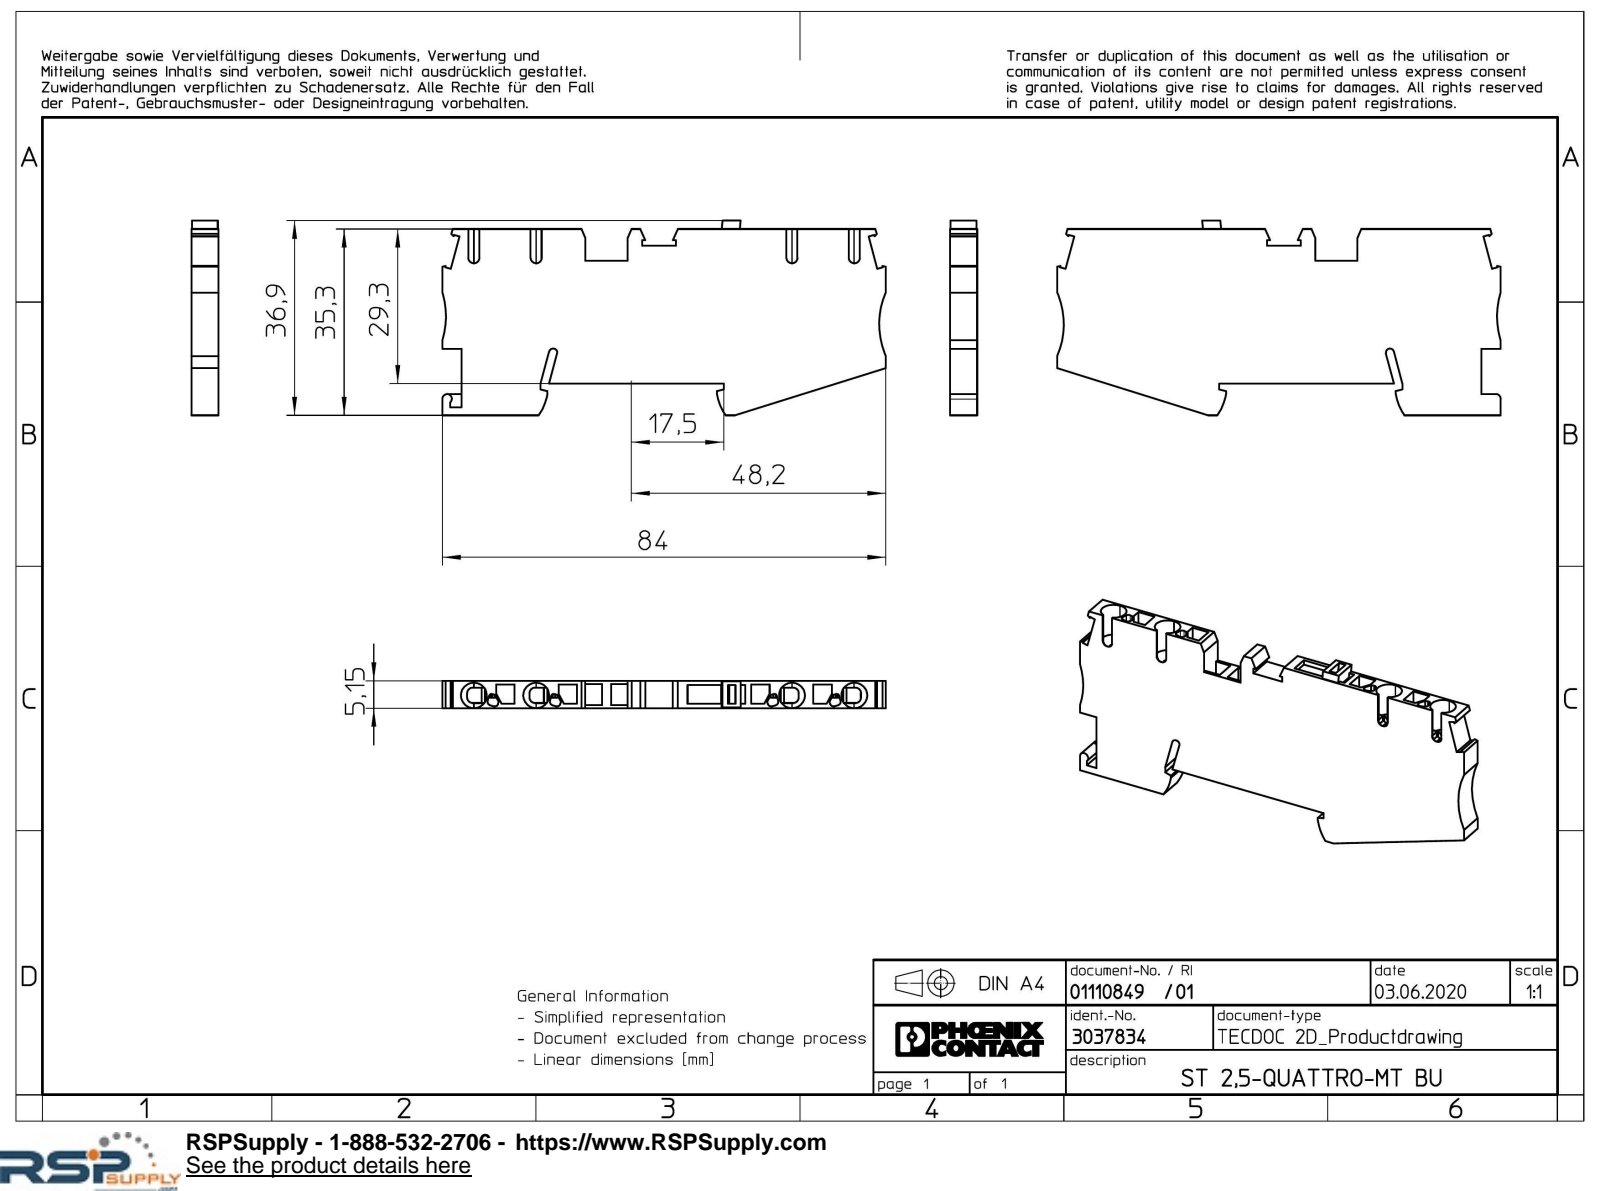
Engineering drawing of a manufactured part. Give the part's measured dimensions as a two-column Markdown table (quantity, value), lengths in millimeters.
| quantity | value |
| --- | --- |
| part name | st25quattro_mt_bu_select |
| STEP written by | Creo Elements/Direct Modeling 20.1A 29-Sep-2018 (C) Parametric Technology GmbH (AUTOMOTIVE_DESIGN) |
| units | millimeters |
| bodies | 1 solid, 279 faces (211 planar, 48 cylindrical, 20 other) |
| overall size | 84 × 36.85 × 5.15 |
| volume | 11 076 mm³ |
| surface area | 8 305 mm² |
| partial cylindrical surfaces (radius × count) | 1 × 16, 2.4 × 8, 0.5 × 4, 0.6 × 4, 0.67 × 4, 9.5 × 2, 15 × 2, 0.2 × 1 |
| main face-to-face distances | 5.15, 0.65, 29.25, 11.8, 6, 4.5, 35.25, 3.15, 4.85, 6.25 |
